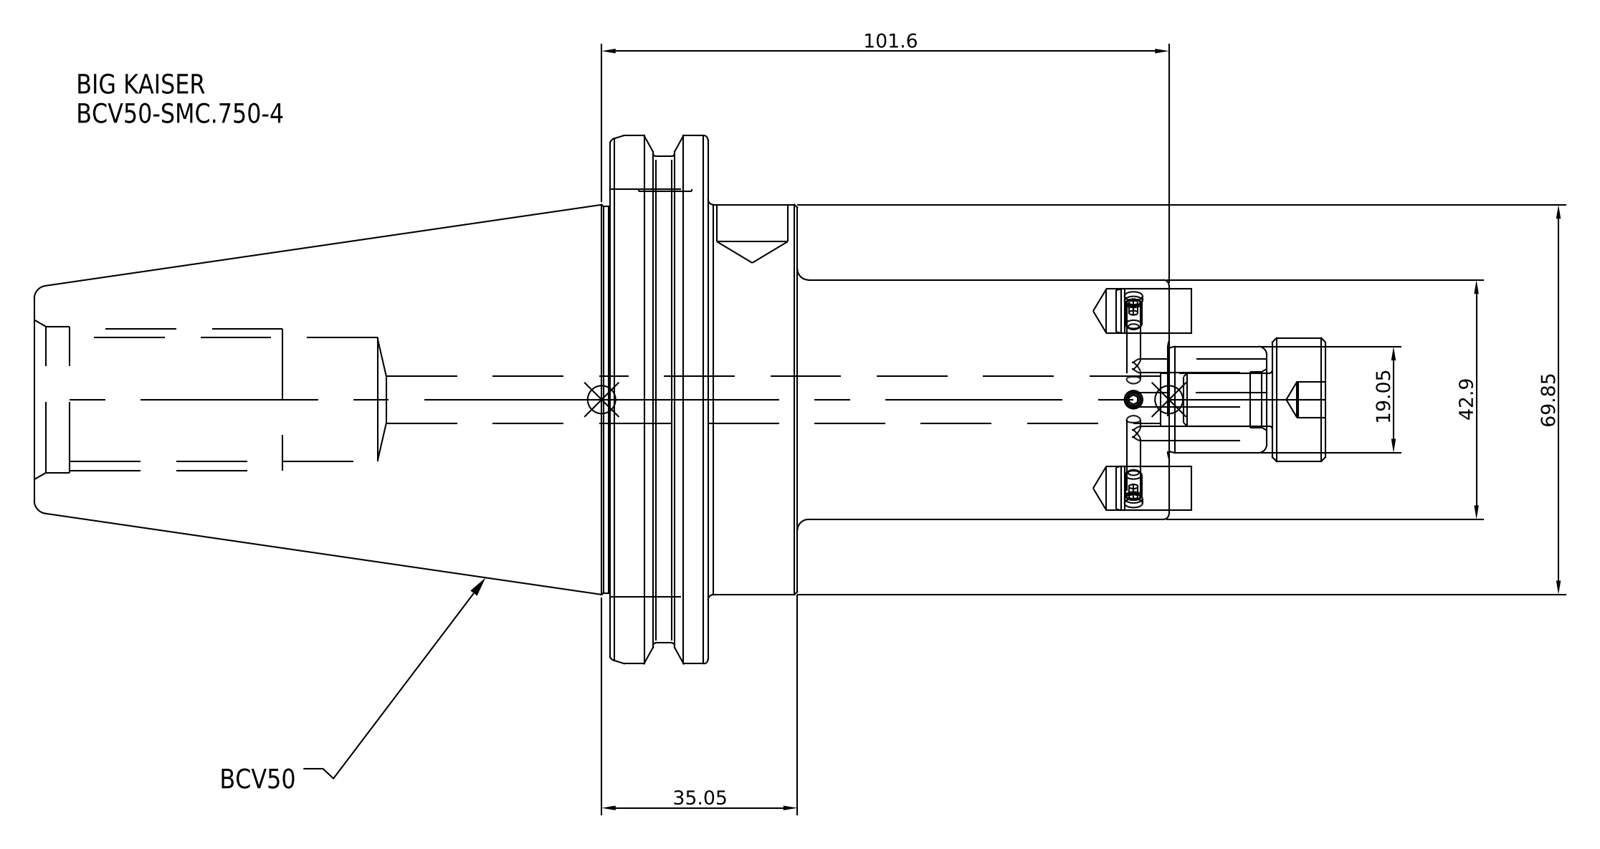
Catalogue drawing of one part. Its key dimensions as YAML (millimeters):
part_name: "BCV50-SMC_750-4"
step_written_by: "SolidWorks 2021 (CONFIG_CONTROL_DESIGN)"
units: millimeters
bodies: {solids: 1, faces: 38, planar: 18, cylindrical: 14, other: 6}
overall_size: [207.16, 98.43, 98.43]
volume: 535654
surface_area: 51967
round_holes:
  - {diameter: 8.43, count: 1}
round_bosses_or_shafts:
  - {diameter: 98.43, count: 1}
  - {diameter: 91.29, count: 1}
  - {diameter: 69.85, count: 1}
  - {diameter: 42.9, count: 1}
face_to_face_distances: [17.55, 16, 33.55, 136.65, 120.65, 103.1, 66.55, 82.55, 100.1, 203.2]
